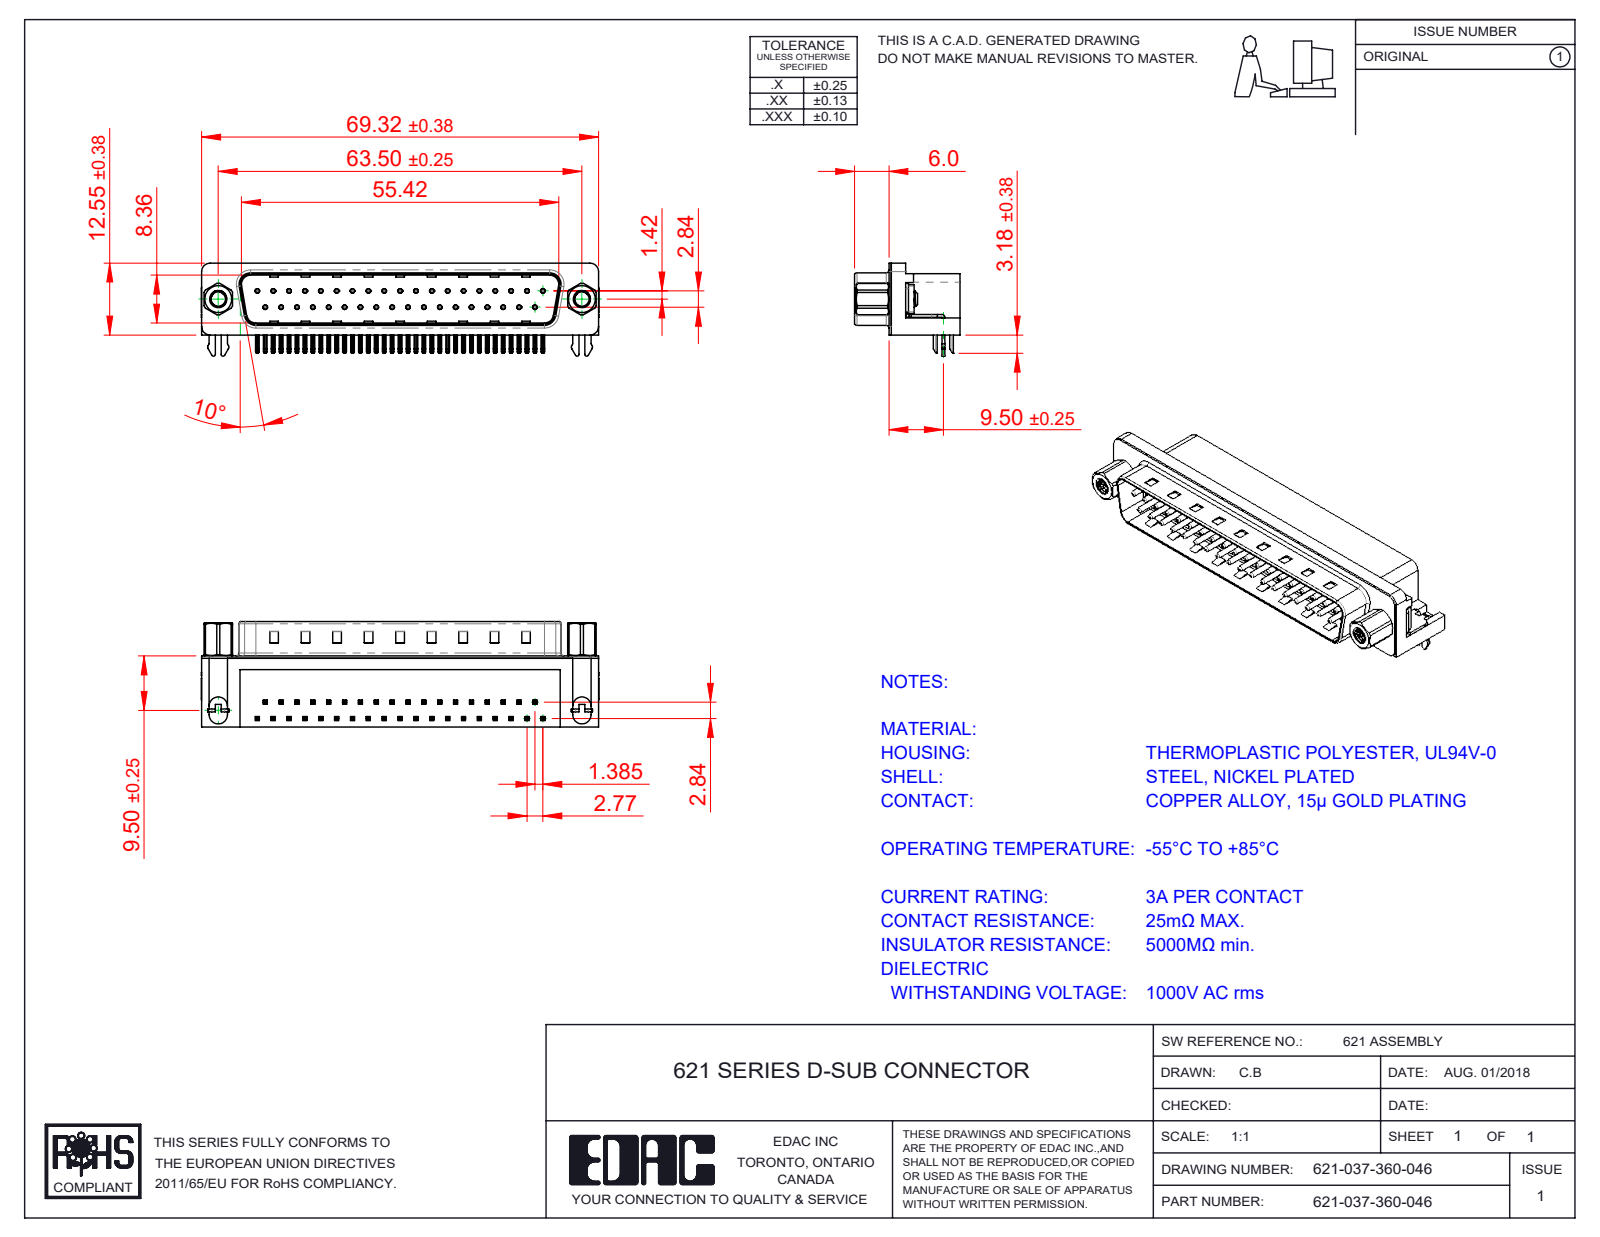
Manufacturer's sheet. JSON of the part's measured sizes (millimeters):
{"part_name": "621 Contact Bottom; 621 4 Prong Board Lock; 621 M3 Hex Standoff 5; 621 M3 Threaded Rivet (+4 more)", "step_written_by": "SolidWorks 2016 (CONFIG_CONTROL_DESIGN)", "units": "millimeters", "bodies": {"solids": 45, "faces": 3467, "planar": 2077, "cylindrical": 1017, "other": 373}, "overall_size": [69.4, 18.4, 16.25], "volume_mm3": 8870, "surface_area_mm2": 10701, "round_holes": [[0.35, 37], [0.8, 37], [2, 2], [2.5, 2], [4, 2], [4.8, 2], [5, 2]], "round_bosses_or_shafts": [[0.75, 37], [3, 4], [4.9, 2], [4.75, 2], [3.9, 2]], "partial_cylinders_radius": [[0.25, 160], [0.12, 74], [1, 16], [0.5, 9], [1.6, 8], [1.5, 7], [0.9, 4], [2, 4]], "face_to_face_distances": [0.4, 12, 10.35, 8.76, 2.1, 1.7, 10.46, 10.86, 9, 12.4], "hole_center_spacings": [3.16, 2.77, 5.54, 8.31, 11.08, 13.85, 19.39, 22.16]}
